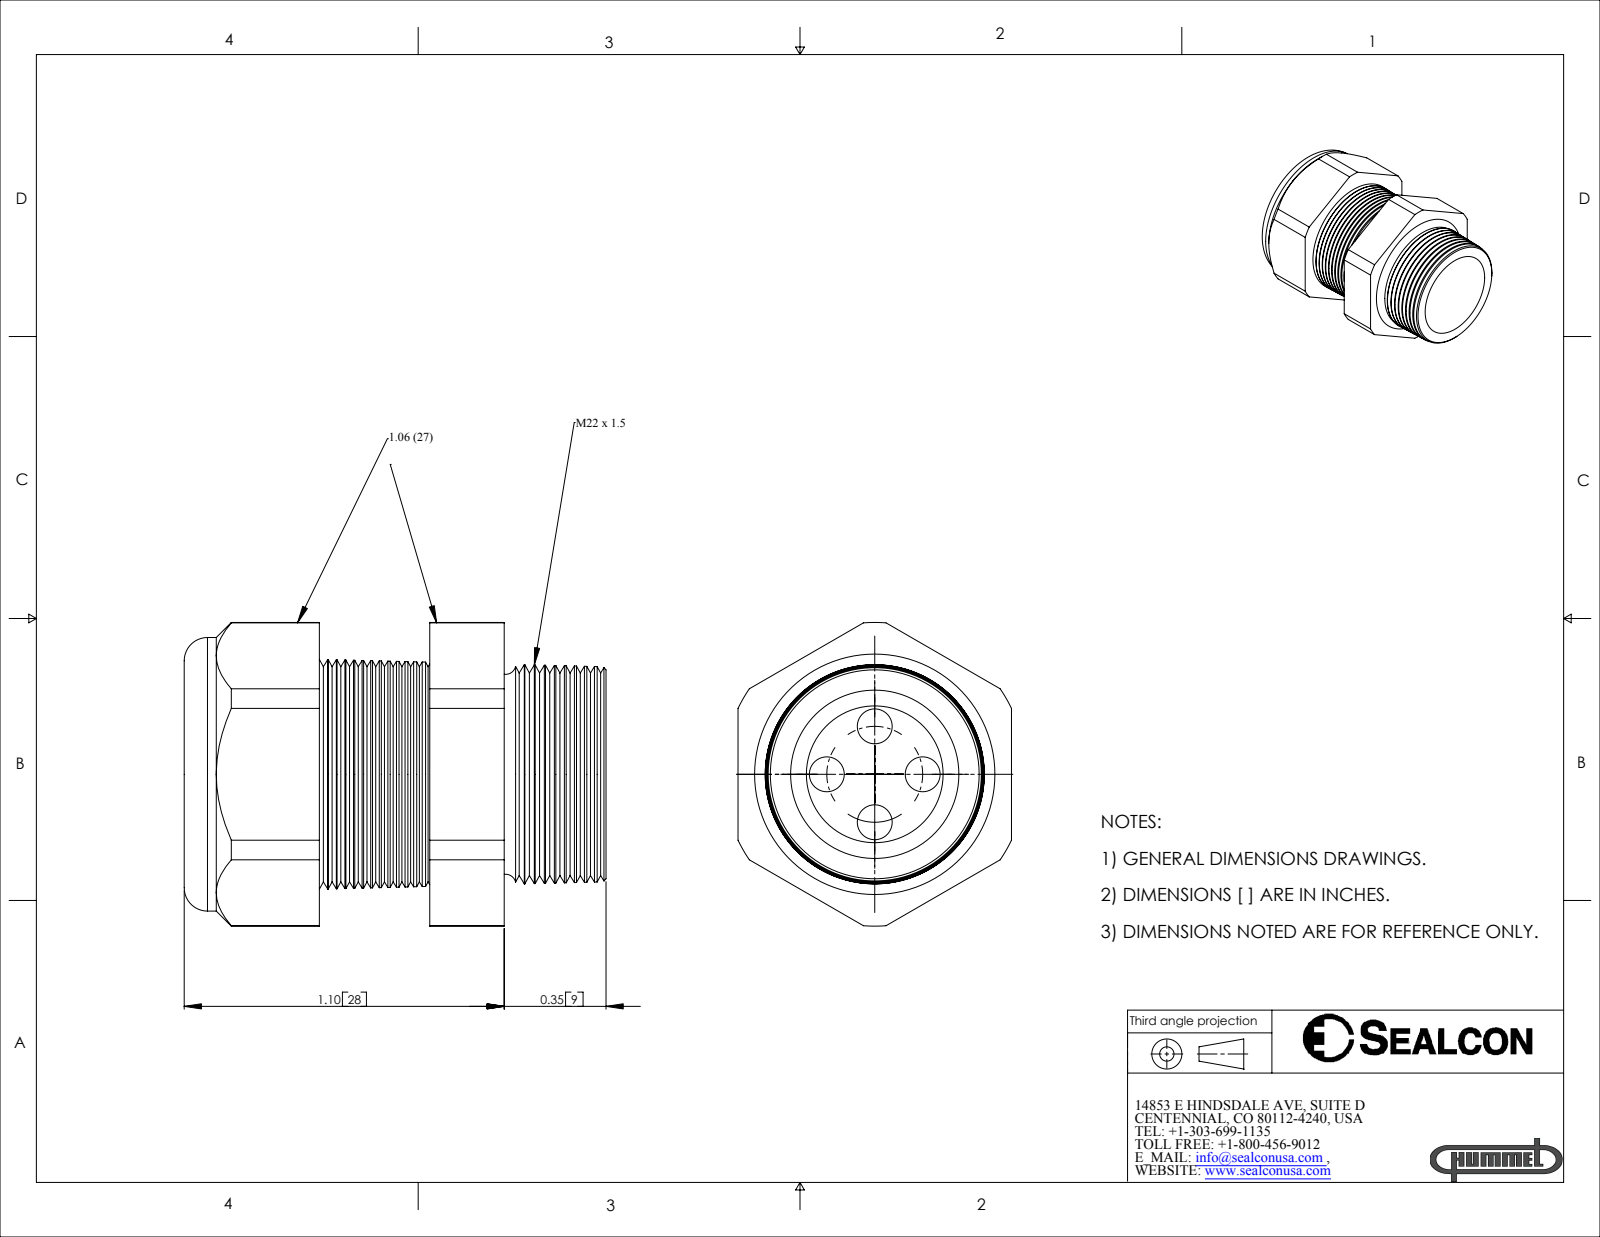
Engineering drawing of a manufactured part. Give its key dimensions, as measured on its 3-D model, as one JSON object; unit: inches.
{"part_name": "CD22M9-GY", "step_written_by": "SolidWorks 2007 (CONFIG_CONTROL_DESIGN)", "units": "inches", "bodies": {"solids": 2, "faces": 194, "planar": 20, "cylindrical": 28, "other": 146}, "overall_size": [1.45, 1.043, 0.94], "volume_in3": 0.584, "surface_area_in2": 10.28, "round_holes": [[0.12, 4], [0.45, 1], [0.47, 1]], "round_bosses_or_shafts": [[0.94, 1]], "partial_cylinders_radius": [[0.522, 1]], "face_to_face_distances": [0.94, 0.844, 0.465, 0.38, 1.1, 0.635, 0.256, 1.45, 0.985, 0.606], "hole_center_spacings": [0.165, 0.233, 0.329]}
